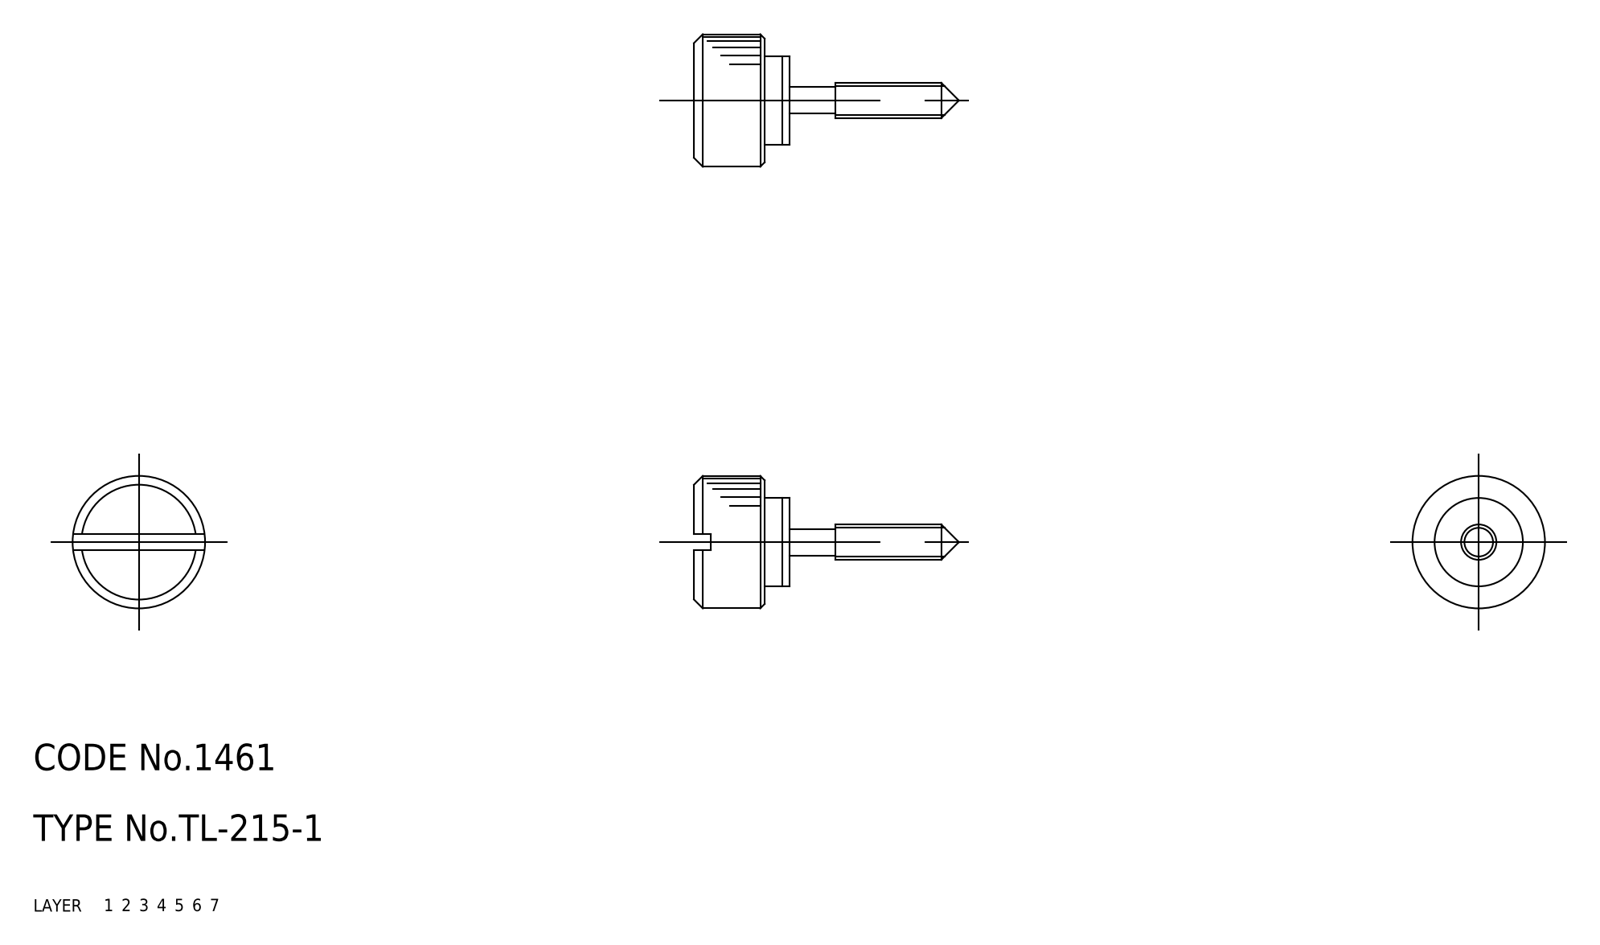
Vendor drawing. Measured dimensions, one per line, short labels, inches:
name: washer; knob; TL_215_1_25727_36
written by: CADfix (AUTOMOTIVE_DESIGN)
unit: in
bodies: 2 solids, 38 faces (0 planar, 0 cylindrical, 38 other)
size: 1.181 × 0.591 × 0.591
volume: 0.107 in³; area: 1.848 in²
